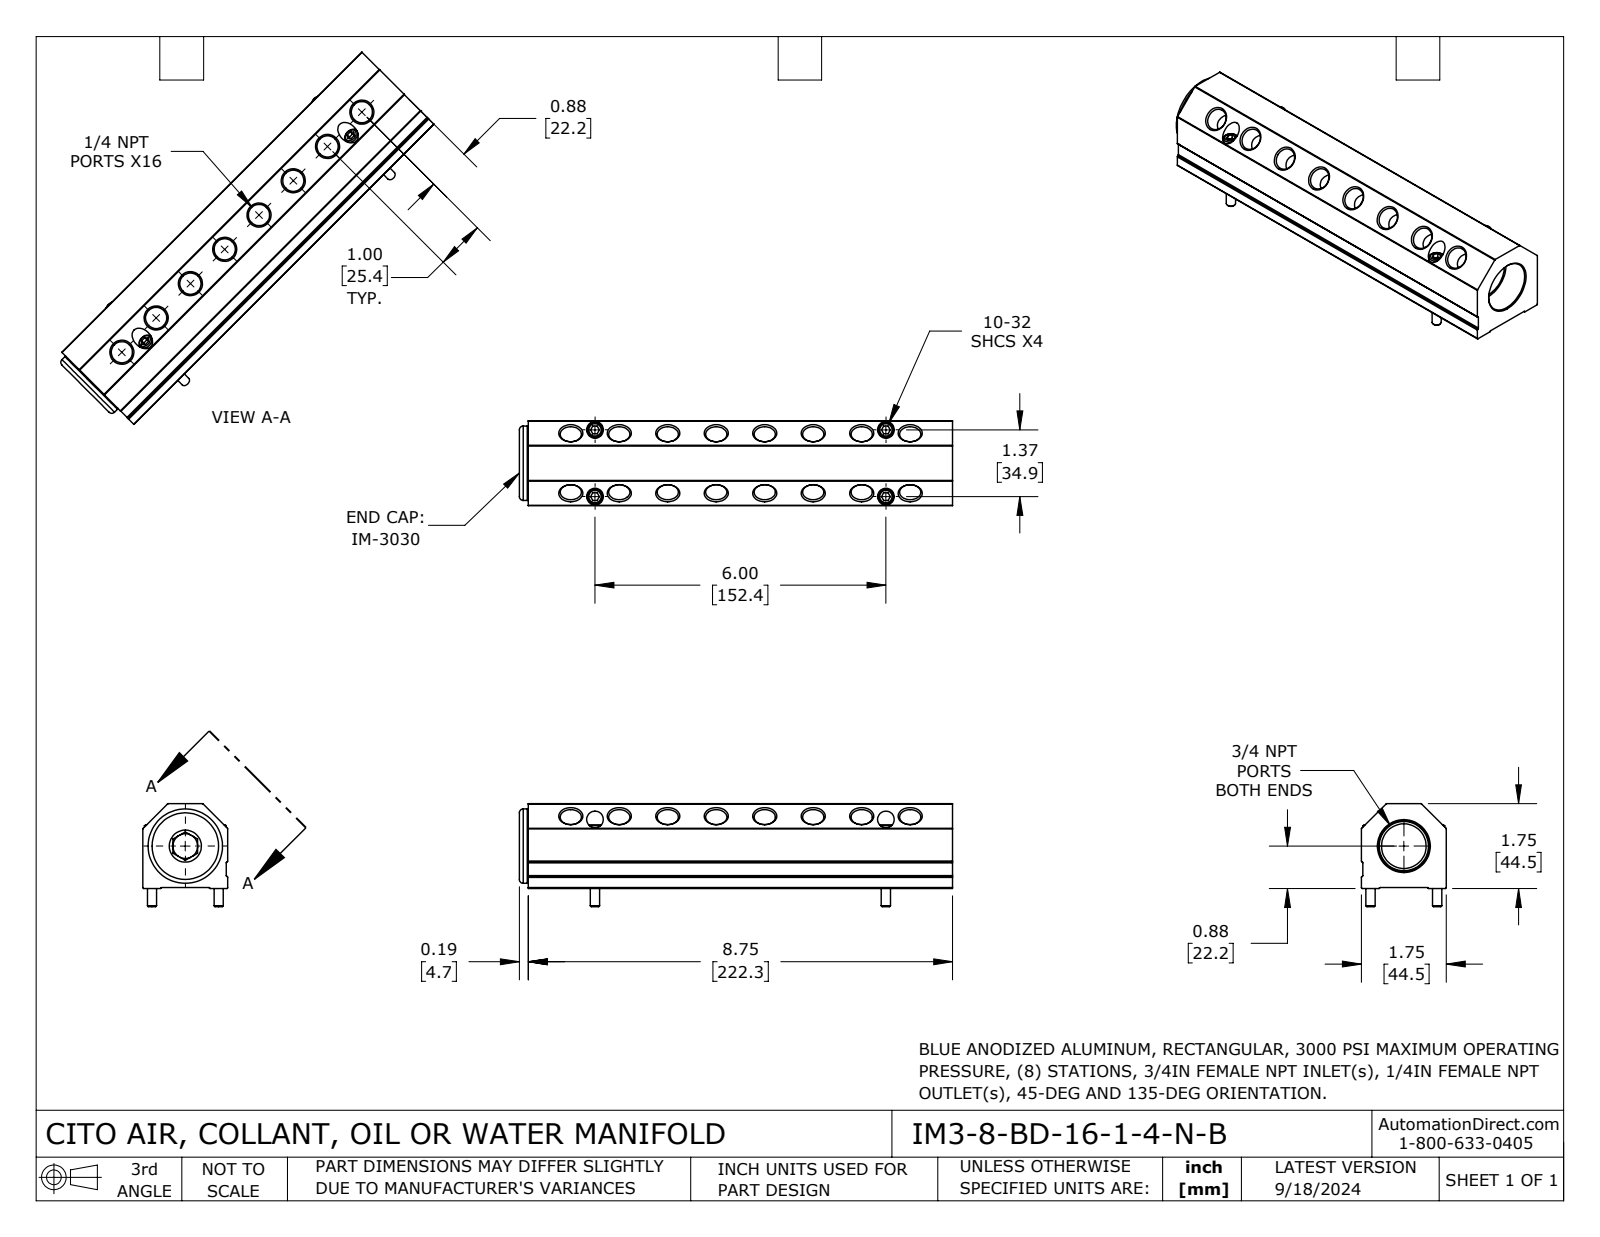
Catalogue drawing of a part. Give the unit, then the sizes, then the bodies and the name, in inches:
Units: inches
Overall size (bounding box): 8.935 × 2.125 × 1.75
Round holes (diameter × count): ⌀0.437 ×16, ⌀0.203 ×4, ⌀0.344 ×4, ⌀0.51 ×1, ⌀0.921 ×1, ⌀1.394 ×1
Round bosses / shafts (diameter × count): ⌀0.312 ×4, ⌀0.19 ×4, ⌀1.534 ×1, ⌀1.182 ×1, ⌀0.938 ×1
Partial cylindrical surfaces — rounded edges, fillets, slot ends (radius × count): R0.02 ×14
Main face-to-face distances: 1.75, 1.73, 0.02, 1.75, 0.03, 1.72, 8.75, 0.185, 8.935, 0.531
Hole centre spacings: 1, 2, 3, 4, 5, 6, 1.375, 6.156
Volume: 17.63 in³ · Surface area: 106.1 in²
Bodies: 6 solids, 248 faces (82 planar, 90 cylindrical, 76 other)
Part name (STEP PRODUCT): IM3-8-BD-16-1-4-N-B
STEP written by: SolidWorks 2023 (CONFIG_CONTROL_DESIGN)
